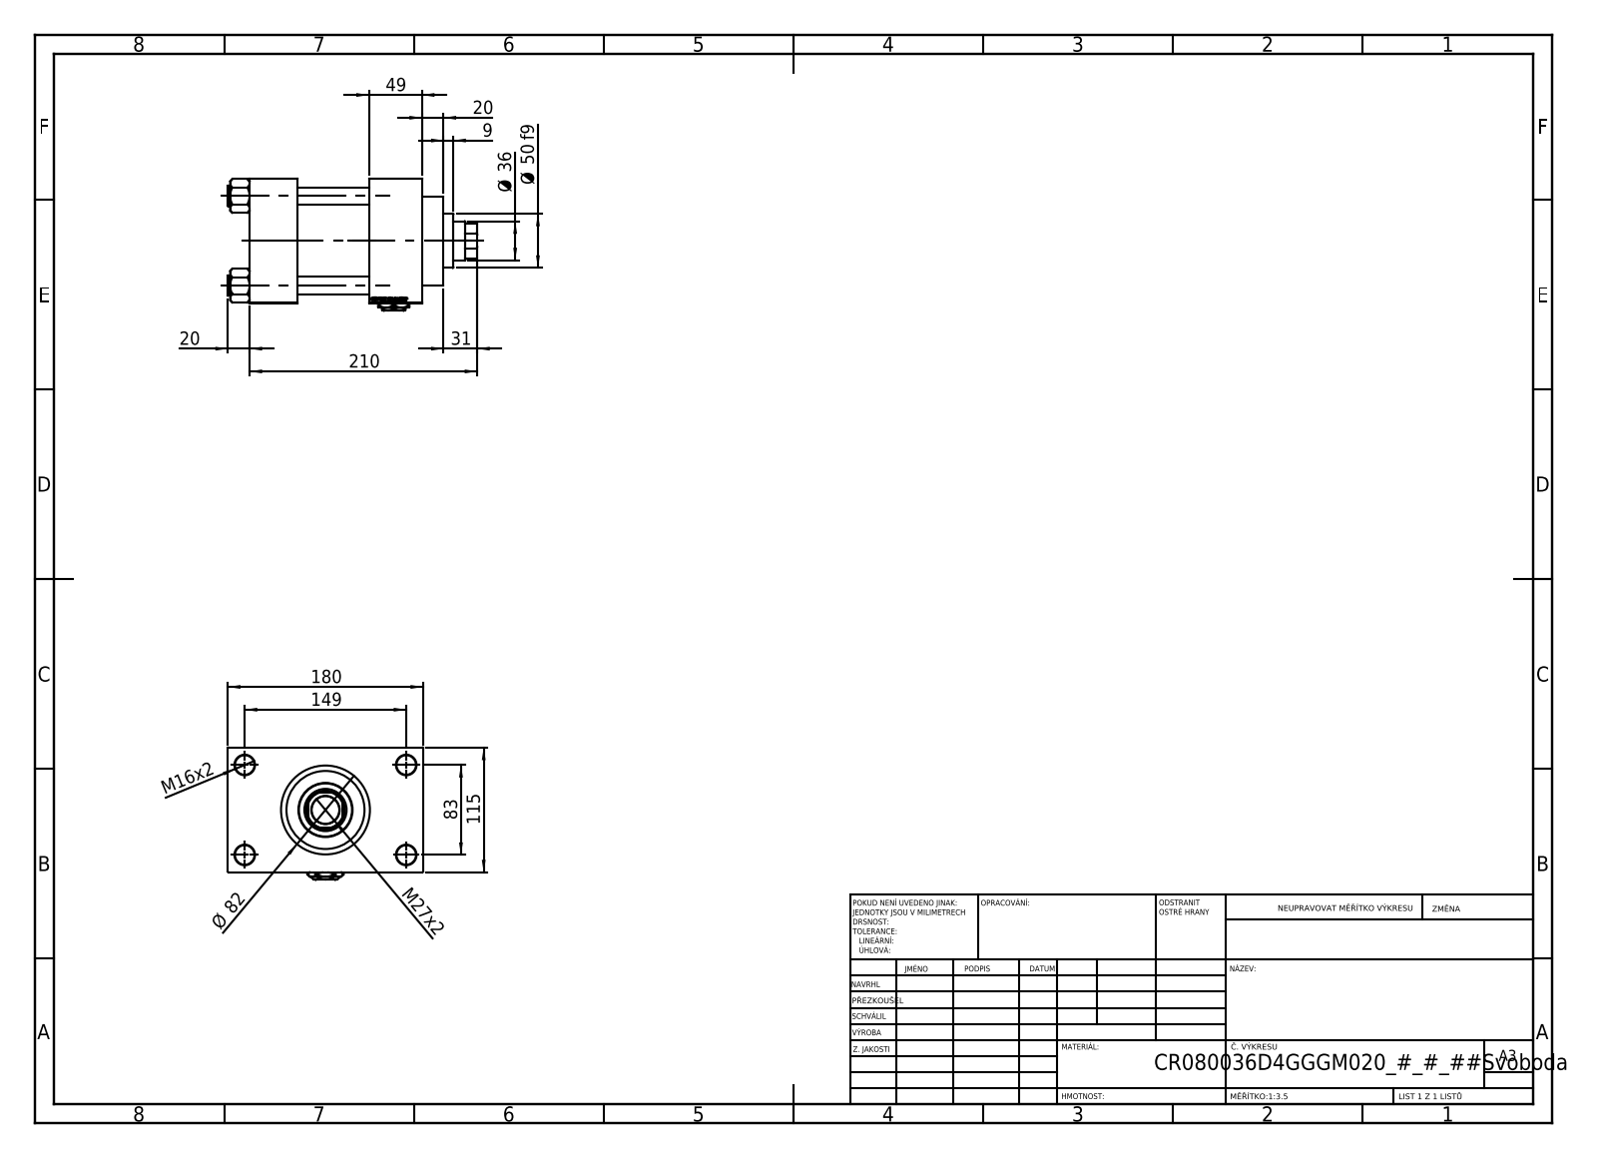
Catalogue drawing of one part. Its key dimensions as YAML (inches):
part_name: "NUT_M5_D; Zatka_pro_OIL_PORT; V215CR_VCP_D; V215_VC_A (+2 more)"
step_written_by: "SolidWorks 2019 (CONFIG_CONTROL_DESIGN)"
units: inches
bodies: {solids: 12, faces: 1200, planar: 569, cylindrical: 93, other: 538}
overall_size: [9.055, 7.087, 4.803]
volume: 121.3
surface_area: 460.1
round_holes:
  - {diameter: 0.63, count: 4}
  - {diameter: 0.709, count: 4}
  - {diameter: 0.276, count: 2}
  - {diameter: 1.041, count: 2}
  - {diameter: 1.378, count: 2}
  - {diameter: 1.004, count: 1}
  - {diameter: 1.417, count: 1}
  - {diameter: 1.535, count: 1}
  - {diameter: 2.402, count: 1}
  - {diameter: 2.835, count: 1}
  - {diameter: 3.15, count: 1}
round_bosses_or_shafts:
  - {diameter: 0.748, count: 4}
  - {diameter: 3.386, count: 1}
  - {diameter: 3.228, count: 1}
  - {diameter: 1.969, count: 1}
partial_cylinders:
  - {radius: 0.689, count: 1}
face_to_face_distances: [4.528, 2.598, 4.331, 1.929, 1.732, 6.26, 5.807, 1.28, 0.787, 2.717]
hole_center_spacings: [1.305, 2.302, 3.256, 3.357, 3.513, 4.561, 5.607, 3.268]
